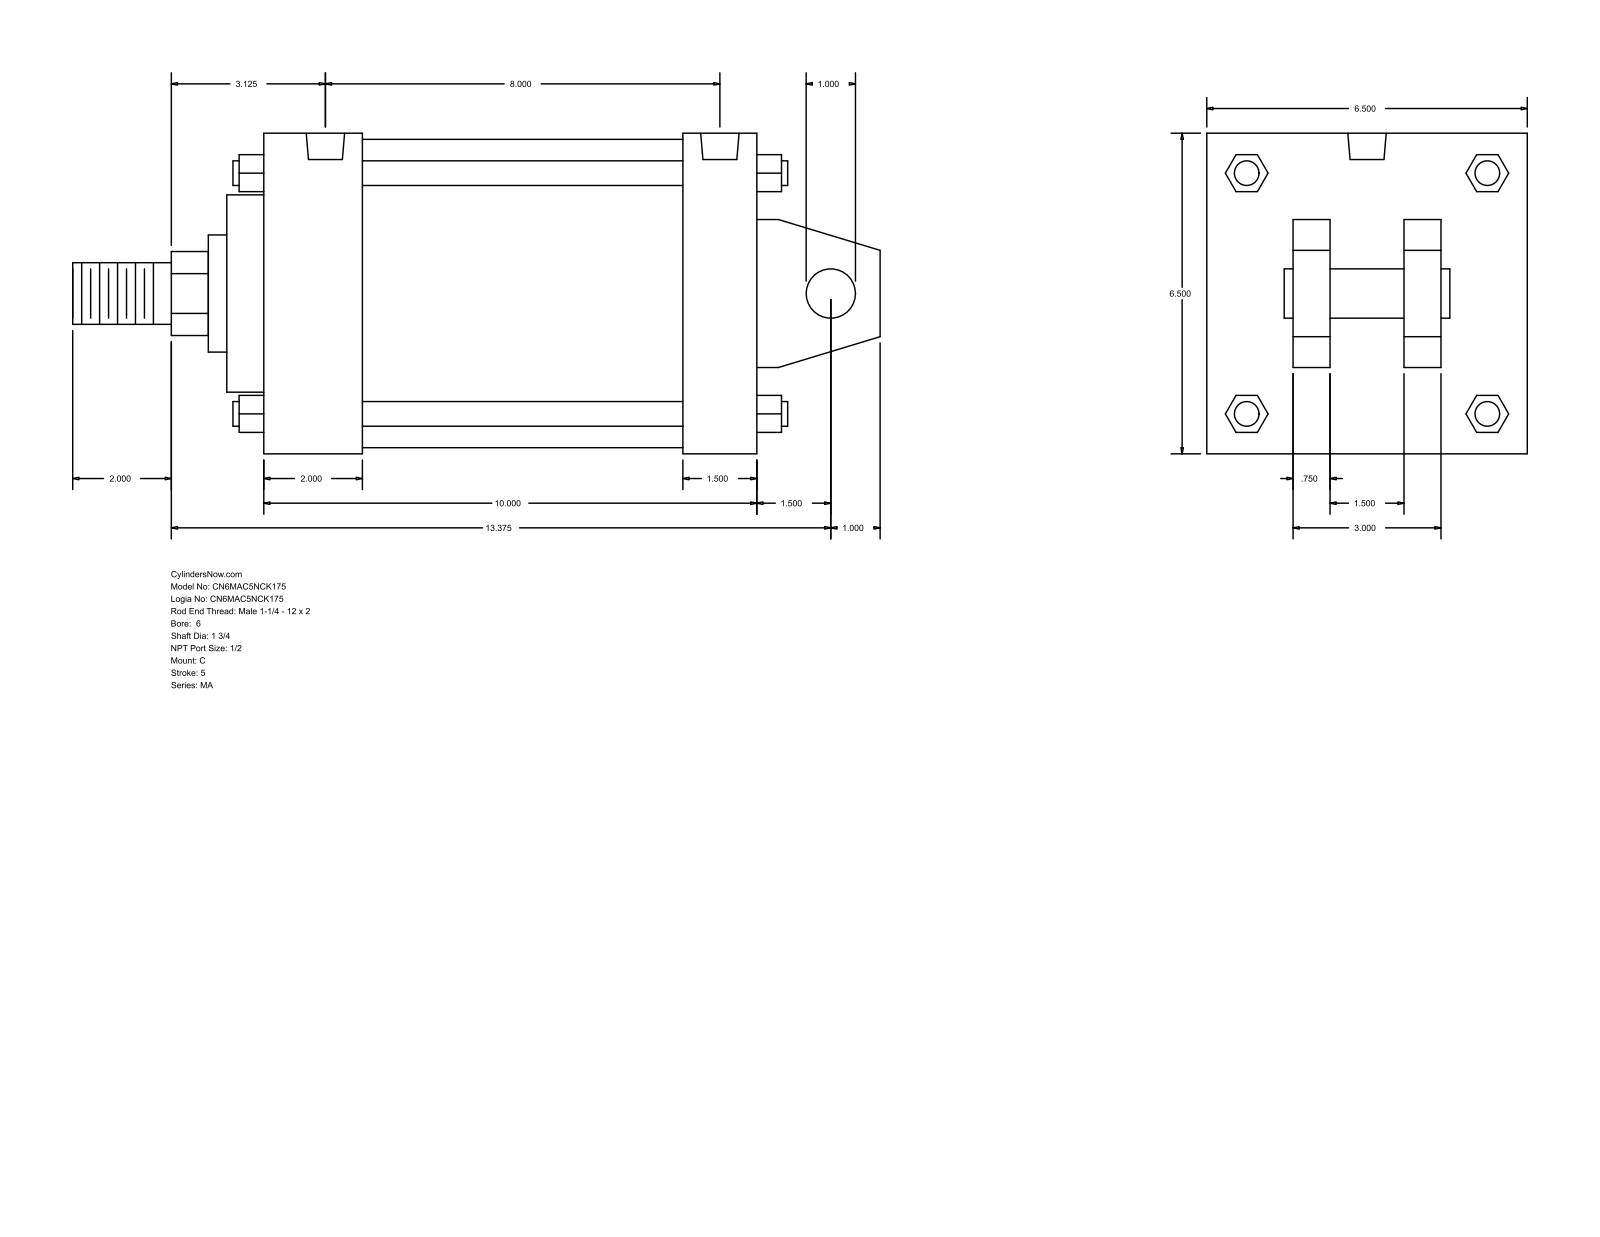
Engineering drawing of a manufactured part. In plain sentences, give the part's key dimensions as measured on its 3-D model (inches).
The part is named "MA_C__0600_1.75". Its 3-D file was written by "GSSL Pune (CONFIG_CONTROL_DESIGN)". It is 0 solids with 141 faces: 109 planar, 32 cylindrical and 0 other. Overall it measures 16.375 by 6.5 by 6.5 inches. Round holes: 4 of diameter 0.687, 2 of diameter 0.778. Round bosses or shafts: 4 of diameter 0.5, 1 of diameter 6.25, 1 of diameter 4, 1 of diameter 2.375, 1 of diameter 1.75, 1 of diameter 1.25, 1 of diameter 1. Partial cylindrical surfaces (rounded edges, fillets, slot ends): 1 of radius 0.852. The main face-to-face distances are 6.5, 10, 0.75, 1.5, 2.5, 4, 2, 4.75, 1.75, 8.5. The hole center spacings are 8.
